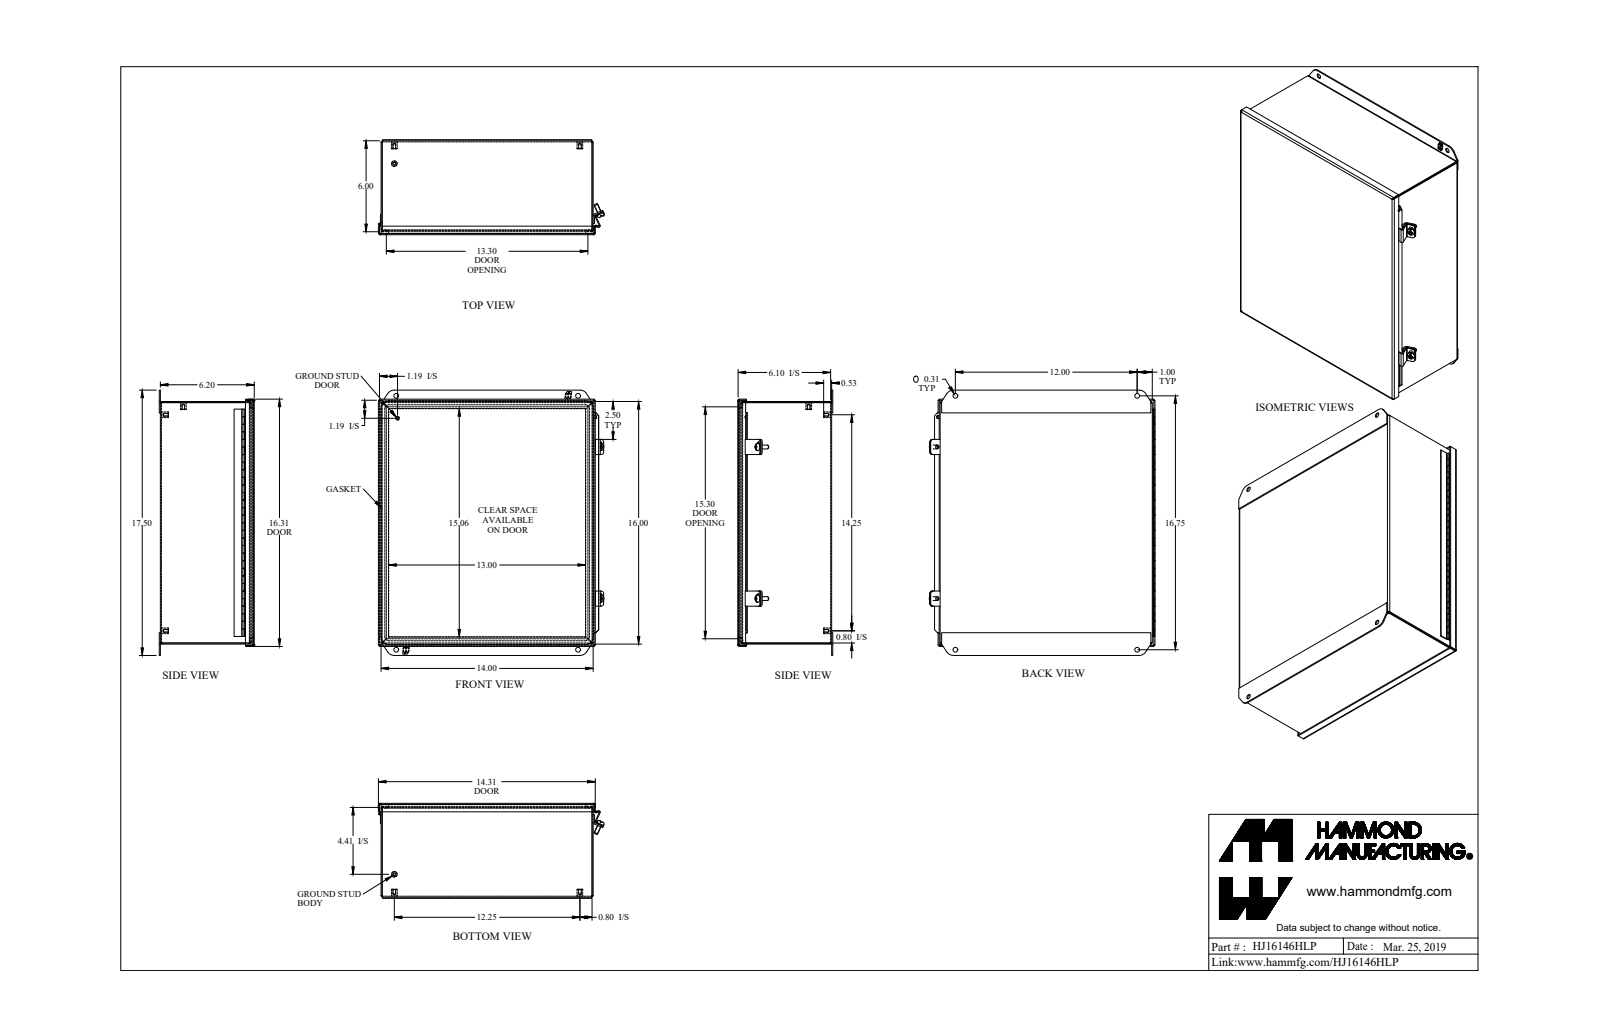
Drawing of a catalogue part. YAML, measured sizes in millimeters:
part_name: "HJ16146HLP"
step_written_by: "SolidWorks 2018 (AUTOMOTIVE_DESIGN)"
units: millimeters
bodies: {solids: 20, faces: 841, planar: 446, cylindrical: 267, other: 128}
overall_size: [444.5, 378.4, 159.2]
volume: 1172000
surface_area: 1293000
round_holes:
  - {diameter: 4, count: 5}
  - {diameter: 8, count: 4}
  - {diameter: 5.4, count: 2}
  - {diameter: 1.3, count: 1}
round_bosses_or_shafts:
  - {diameter: 9.5, count: 5}
  - {diameter: 6.4, count: 3}
  - {diameter: 12.2, count: 2}
  - {diameter: 4.8, count: 1}
  - {diameter: 2.5, count: 1}
  - {diameter: 1.1, count: 1}
partial_cylinders:
  - {radius: 6.4, count: 16}
  - {radius: 0.9, count: 13}
  - {radius: 2.7, count: 13}
  - {radius: 0.3, count: 4}
  - {radius: 3.6, count: 4}
  - {radius: 4.8, count: 4}
  - {radius: 12.7, count: 4}
  - {radius: 12.7, count: 4}
face_to_face_distances: [1.8, 155.6, 157.4, 153.7, 353.8, 404.6, 351.9, 355.6, 406.4, 402.7]
hole_center_spacings: [31.9, 309.6, 393.7, 499.8, 304.8, 311.2, 362, 425.5]
